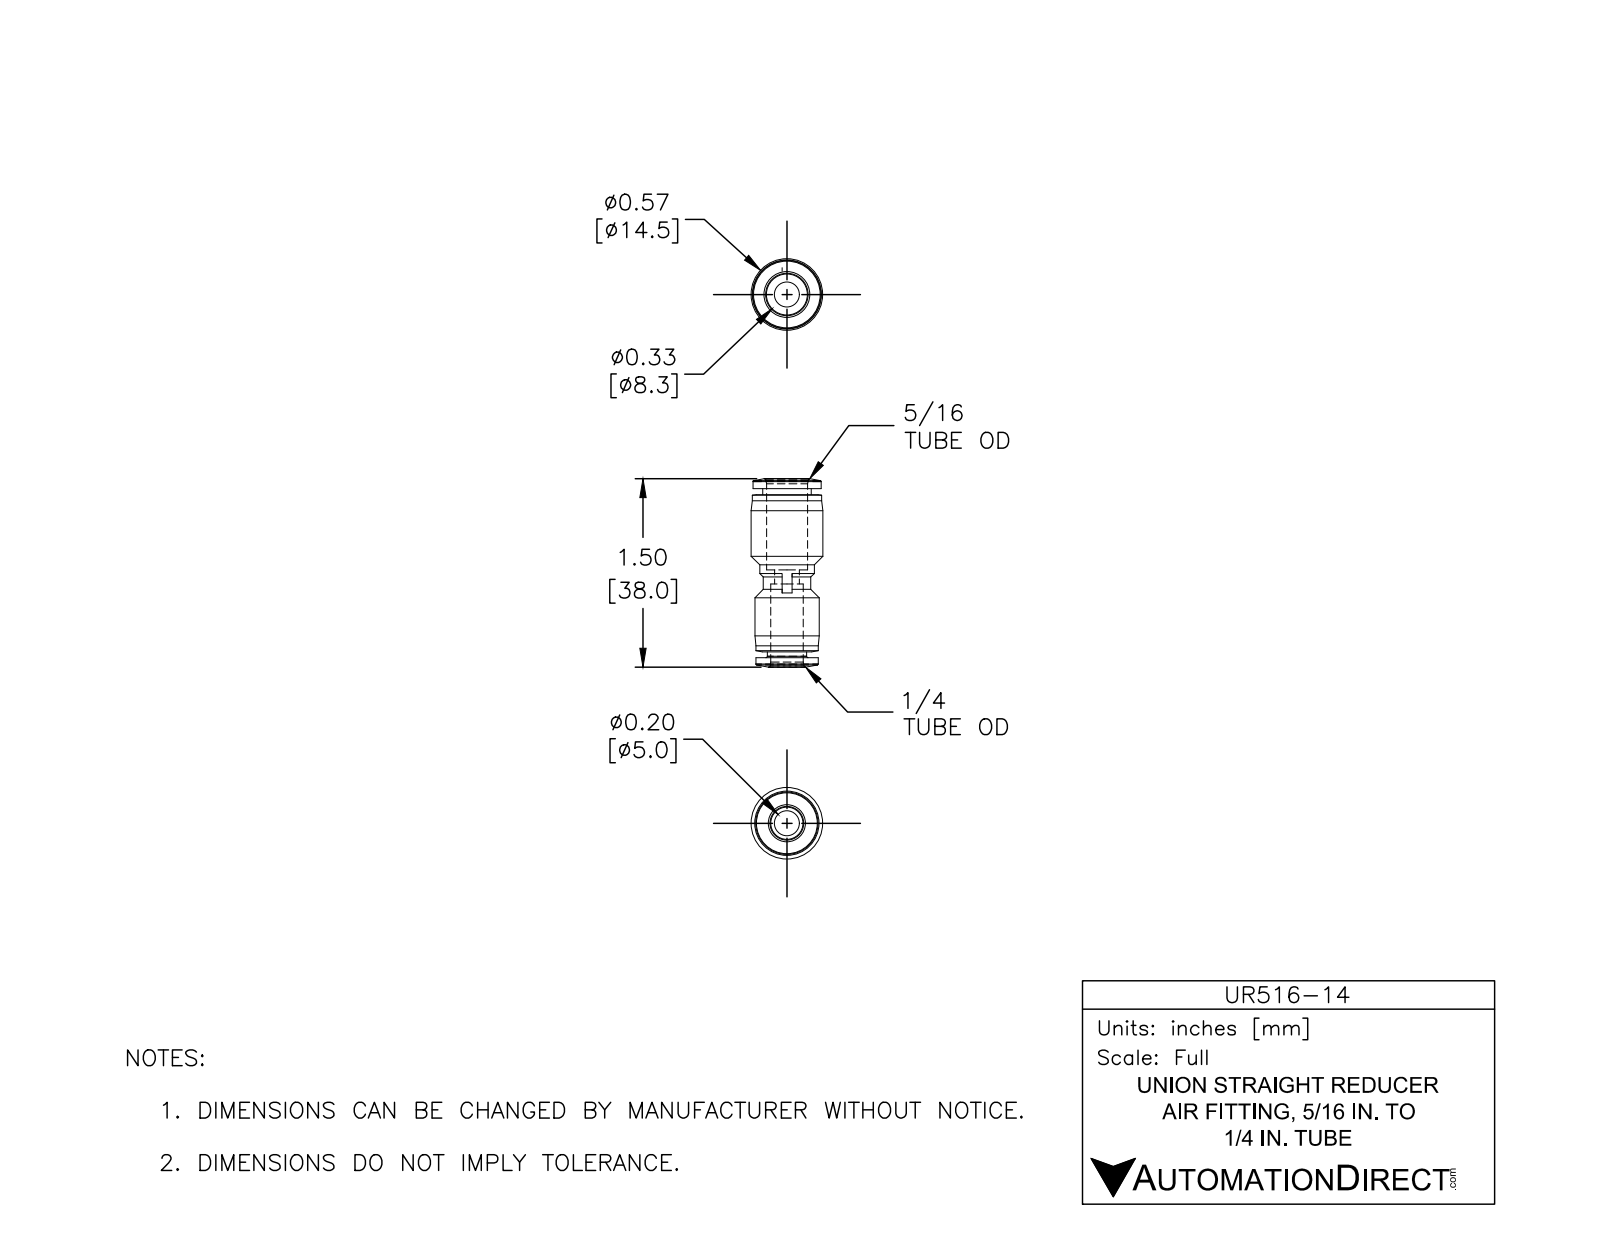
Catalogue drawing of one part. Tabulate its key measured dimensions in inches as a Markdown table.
| quantity | value |
| --- | --- |
| part name | UR516-14 |
| STEP written by | SolidWorks 2015 (CONFIG_CONTROL_DESIGN) |
| units | inches |
| bodies | 1 solid, 68 faces (10 planar, 26 cylindrical, 32 other) |
| overall size | 1.498 × 0.571 × 0.571 |
| volume | 0.201 in³ |
| surface area | 4.554 in² |
| round holes (diameter × count) | 0.197 × 1, 0.258 × 1, 0.327 × 1 |
| round bosses / shafts (diameter × count) | 0.571 × 1, 0.551 × 1, 0.543 × 1, 0.512 × 1, 0.496 × 1, 0.433 × 1, 0.386 × 1, 0.378 × 1 |
| main face-to-face distances | 0.047, 1.297, 1.344, 0.699, 0.598, 0.646, 0.652, 1.25, 0.587, 0.539 |
